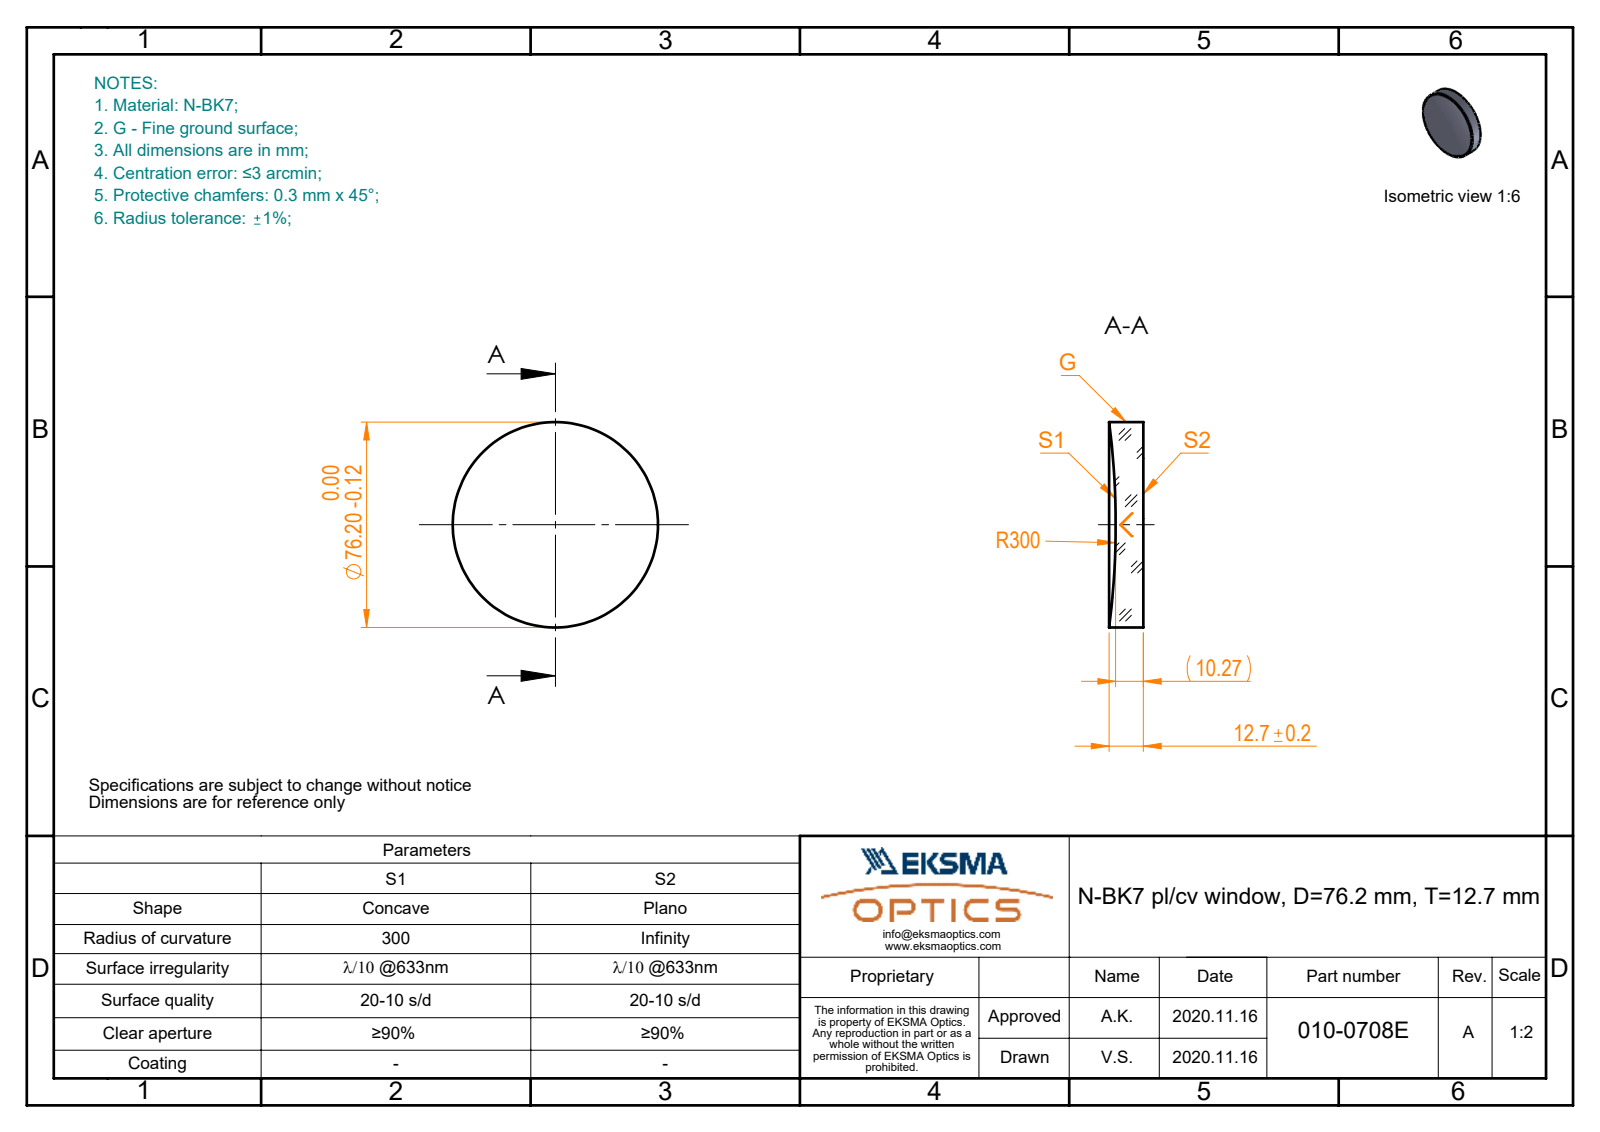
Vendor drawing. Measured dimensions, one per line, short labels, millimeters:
name: 010-0708E_N-BK7_PCV_window
written by: SolidWorks 2019 (CONFIG_CONTROL_DESIGN)
unit: mm
bodies: 1 solid, 5 faces (1 planar, 2 cylindrical, 2 other)
size: 76.2 × 76.2 × 12.7
volume: 52 370 mm³; area: 12 180 mm²
bosses: 1× ⌀76.2
